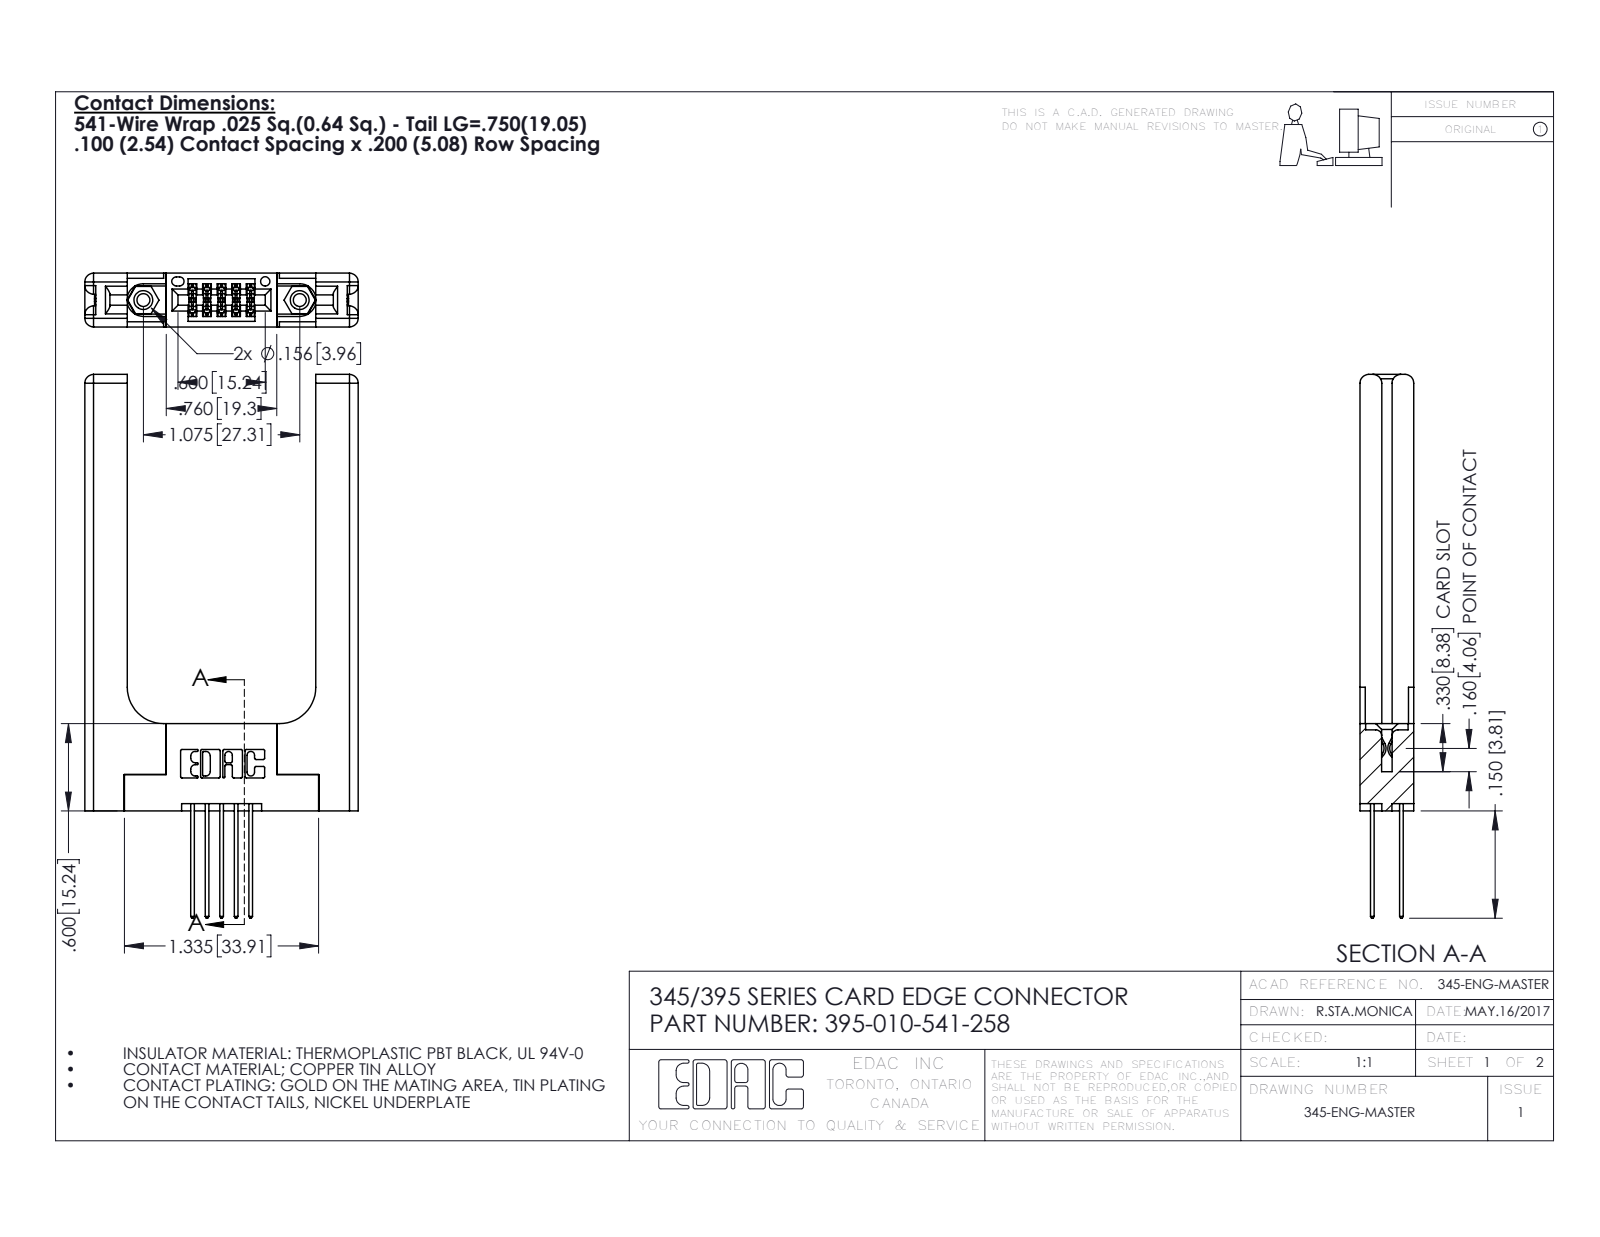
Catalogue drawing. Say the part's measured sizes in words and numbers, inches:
The part is named "345-220-058_345-220-058; 395-010-541-258; 345 Part_Flush Mounting Lugs - 0.156 Dia-TH; 345-292-001_345-293-141 (+1 more)". Its 3-D file was written by "SolidWorks 2016 (CONFIG_CONTROL_DESIGN)". It is 15 solids with 882 faces: 558 planar, 264 cylindrical and 60 other. Overall it measures 3.737 by 1.879 by 0.37 inches. Its volume is 0.783 cubic inches and its surface area 17.12 square inches. Round holes: 2 of diameter 0.089, 2 of diameter 0.125, 2 of diameter 0.156, 1 of diameter 0.064. Round bosses or shafts: 2 of diameter 0.155. Partial cylindrical surfaces (rounded edges, fillets, slot ends): 22 of radius 0.01, 16 of radius 0.06, 15 of radius 0.006, 10 of radius 0.01, 6 of radius 0.007, 6 of radius 0.031, 3 of radius 0.026, 2 of radius 0.014. The main face-to-face distances are 0.37, 0.15, 0.22, 0.072, 0.077, 0.148, 0.298, 1.296, 0.2, 0.071. The hole center spacings are 0.27, 0.847, 1.075.
